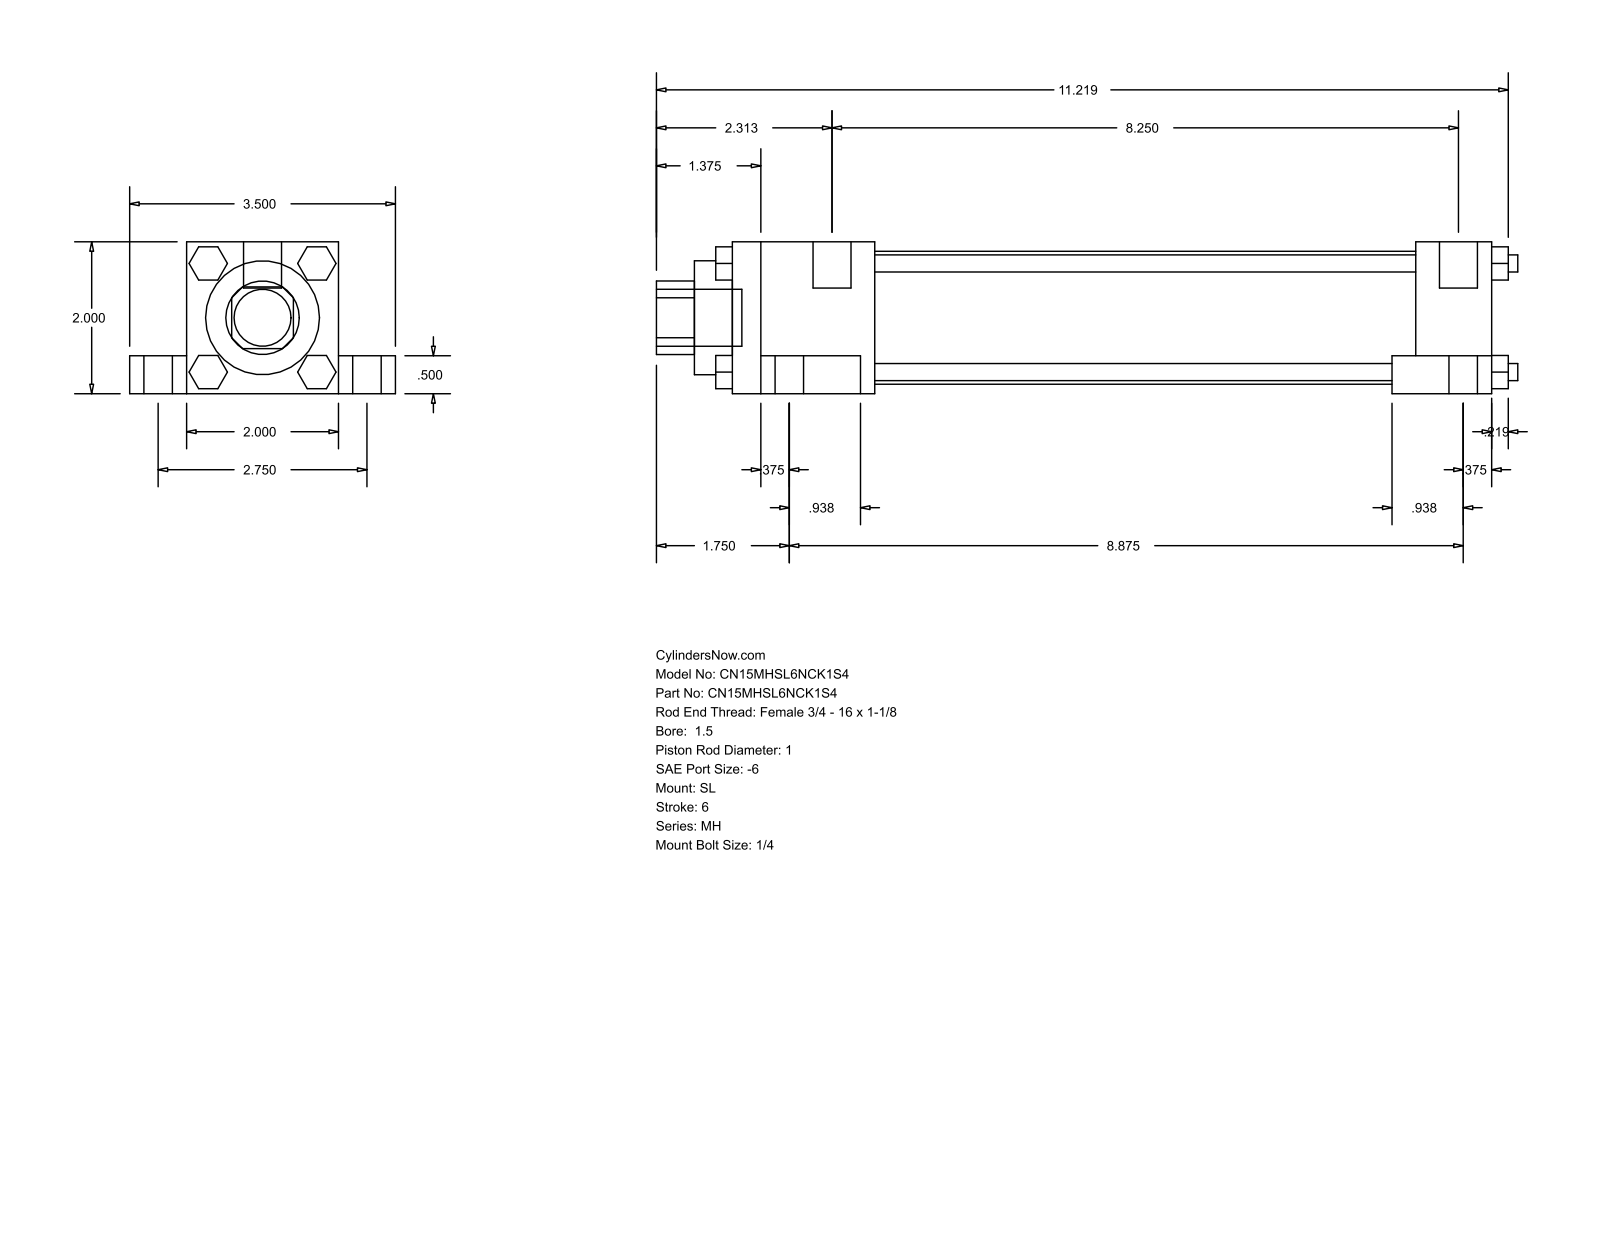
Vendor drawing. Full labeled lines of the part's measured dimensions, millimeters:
Part name (STEP PRODUCT): MH_SL__0150_1
STEP written by: GSSL Pune (CONFIG_CONTROL_DESIGN)
Units: millimetres
Bodies: 0 solids, 148 faces (112 planar, 36 cylindrical, 0 other)
Overall size (bounding box): 288.13 × 88.9 × 50.8
Round holes (diameter × count): ⌀25.4 ×1, ⌀38.1 ×1, ⌀44.45 ×1
Round bosses / shafts (diameter × count): ⌀15.88 ×4, ⌀9.53 ×4, ⌀5.71 ×4, ⌀5.56 ×4, ⌀12.7 ×2, ⌀19.05 ×1
Partial cylindrical surfaces — rounded edges, fillets, slot ends (radius × count): R12.29 ×1
Main face-to-face distances: 50.8, 12.7, 38.1, 19.05, 69.85, 254, 25.4, 9.52, 33.34, 211.14
